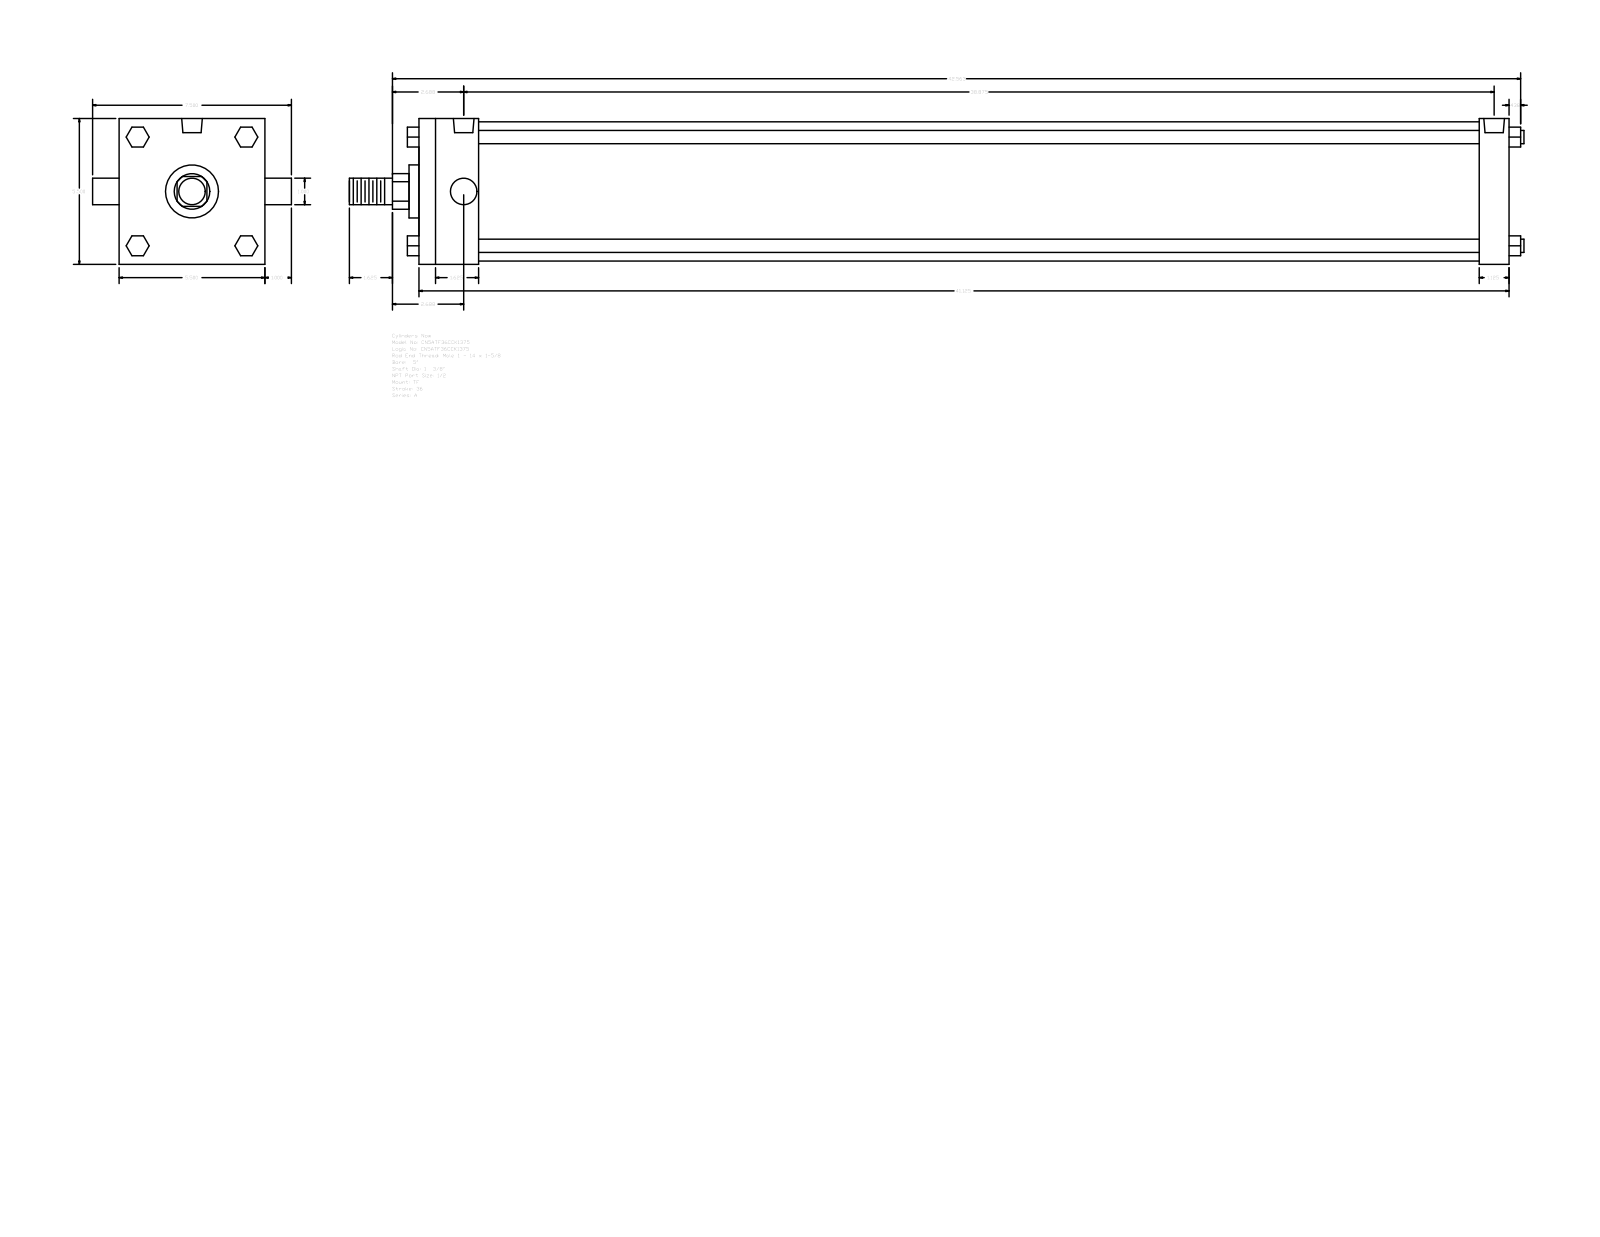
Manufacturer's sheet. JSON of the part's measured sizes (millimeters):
{"part_name": "A_TF__0500_1.375", "step_written_by": "GSSL Pune (CONFIG_CONTROL_DESIGN)", "units": "millimeters", "bodies": {"solids": 0, "faces": 120, "planar": 92, "cylindrical": 28, "other": 0}, "overall_size": [1125.54, 190.5, 139.7], "round_holes": [[8.73, 3], [19.77, 2]], "round_bosses_or_shafts": [[12.7, 4], [25.4, 2], [133.35, 1], [50.8, 1], [34.92, 1]], "partial_cylinders_radius": [[17.06, 1]], "face_to_face_distances": [139.7, 1044.57, 57.15, 1016, 28.57, 958.85, 987.42, 19.05, 52.07, 90.18], "hole_center_spacings": [2.39, 985.04, 982.65, 987.43]}
